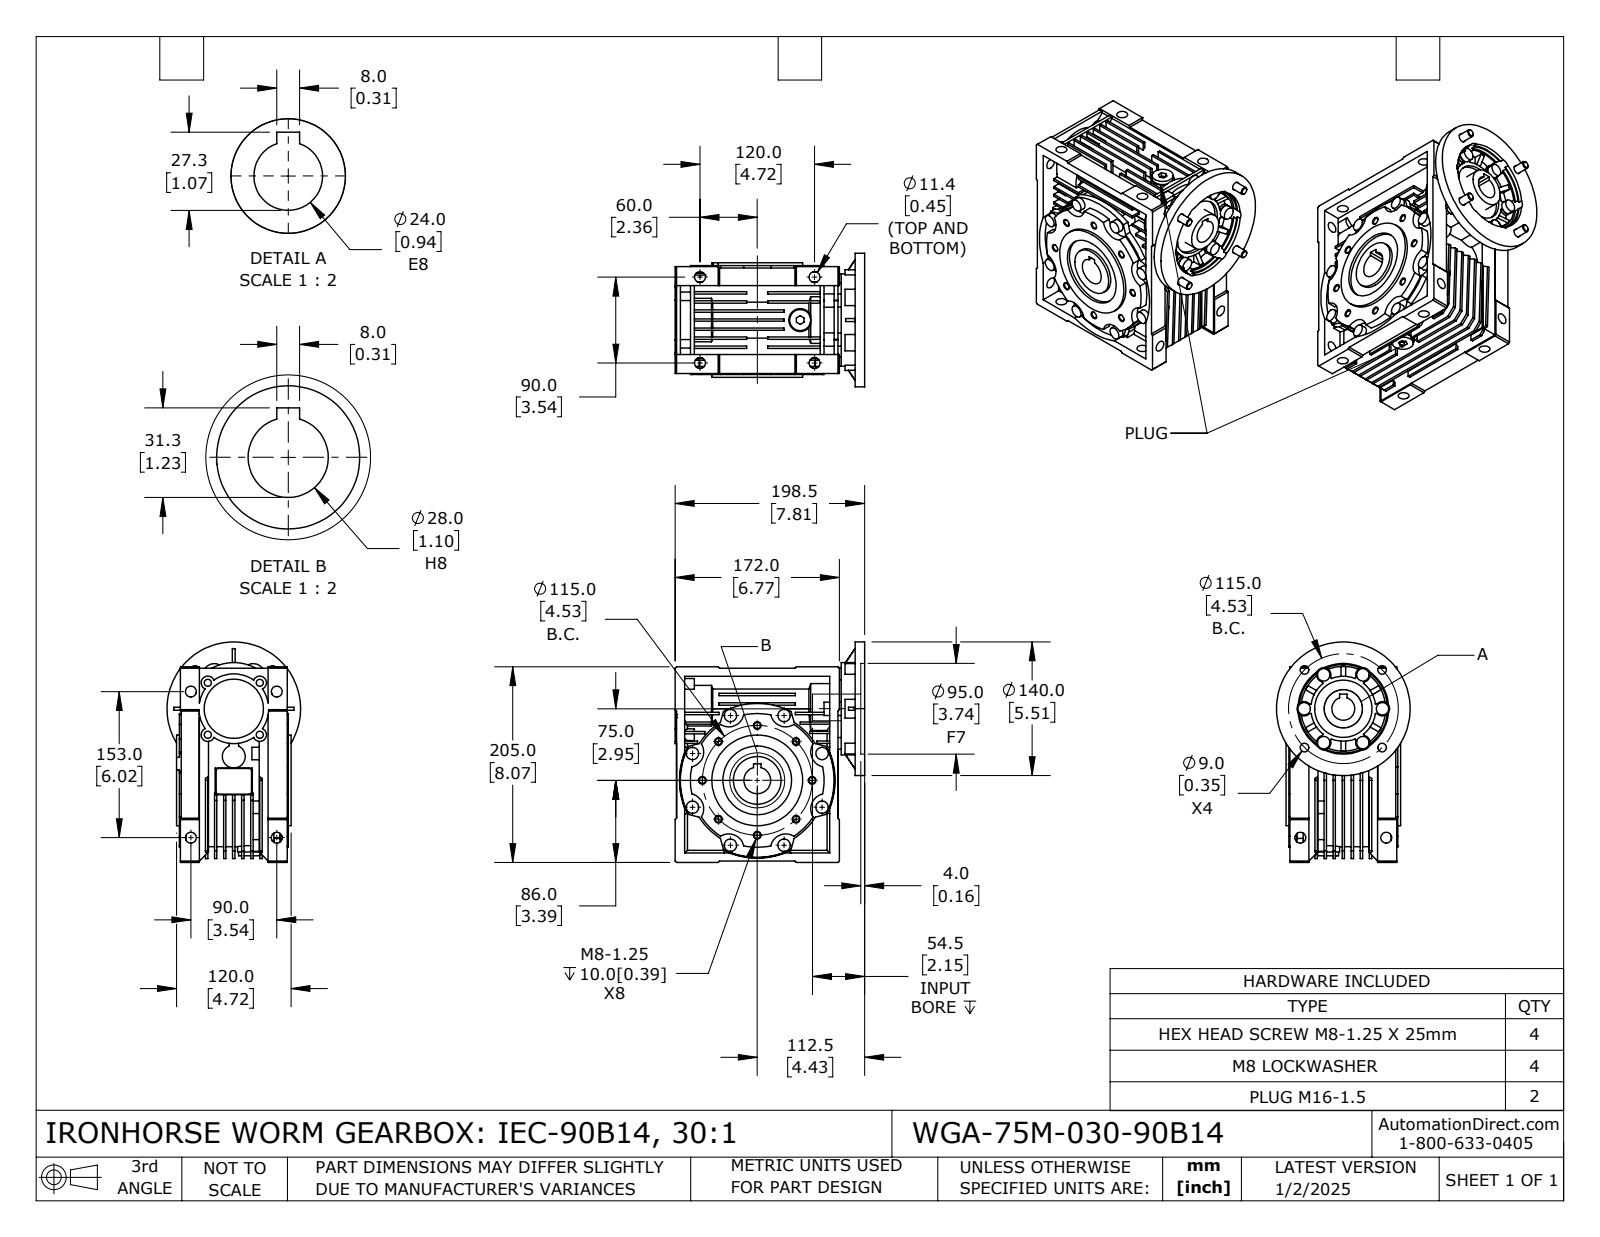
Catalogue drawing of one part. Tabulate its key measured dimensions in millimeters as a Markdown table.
| quantity | value |
| --- | --- |
| part name | WGA-75M-030-90B14 |
| STEP written by | SolidWorks 2024 (CONFIG_CONTROL_DESIGN) |
| units | millimeters |
| bodies | 16 solids, 1349 faces (749 planar, 444 cylindrical, 156 other) |
| overall size | 231 × 211.5 × 140 |
| volume | 2 888 000 mm³ |
| surface area | 496 683 mm² |
| round holes (diameter × count) | 6.65 × 8, 11.38 × 8, 7.45 × 4, 8.2 × 4, 9 × 4, 14.5 × 2, 24 × 1, 25 × 1, 28 × 1, 39 × 1, 42 × 1, 50 × 1 |
| round bosses / shafts (diameter × count) | 13 × 14, 15.4 × 4, 8 × 4, 24 × 3, 22 × 2, 15.8 × 2, 13.7 × 2, 140 × 1 |
| partial cylindrical surfaces (radius × count) | 7 × 10, 16 × 8, 7.5 × 6, 11.75 × 6, 2.5 × 4, 36 × 1, 36.5 × 1, 39 × 1 |
| main face-to-face distances | 9.5, 2.5, 19, 12, 10, 7, 28.5, 16.5, 27.75, 21.5 |
| hole center spacings | 57.5, 81.32, 44.01, 69.2, 106.25, 115, 19.01, 38.49 |
